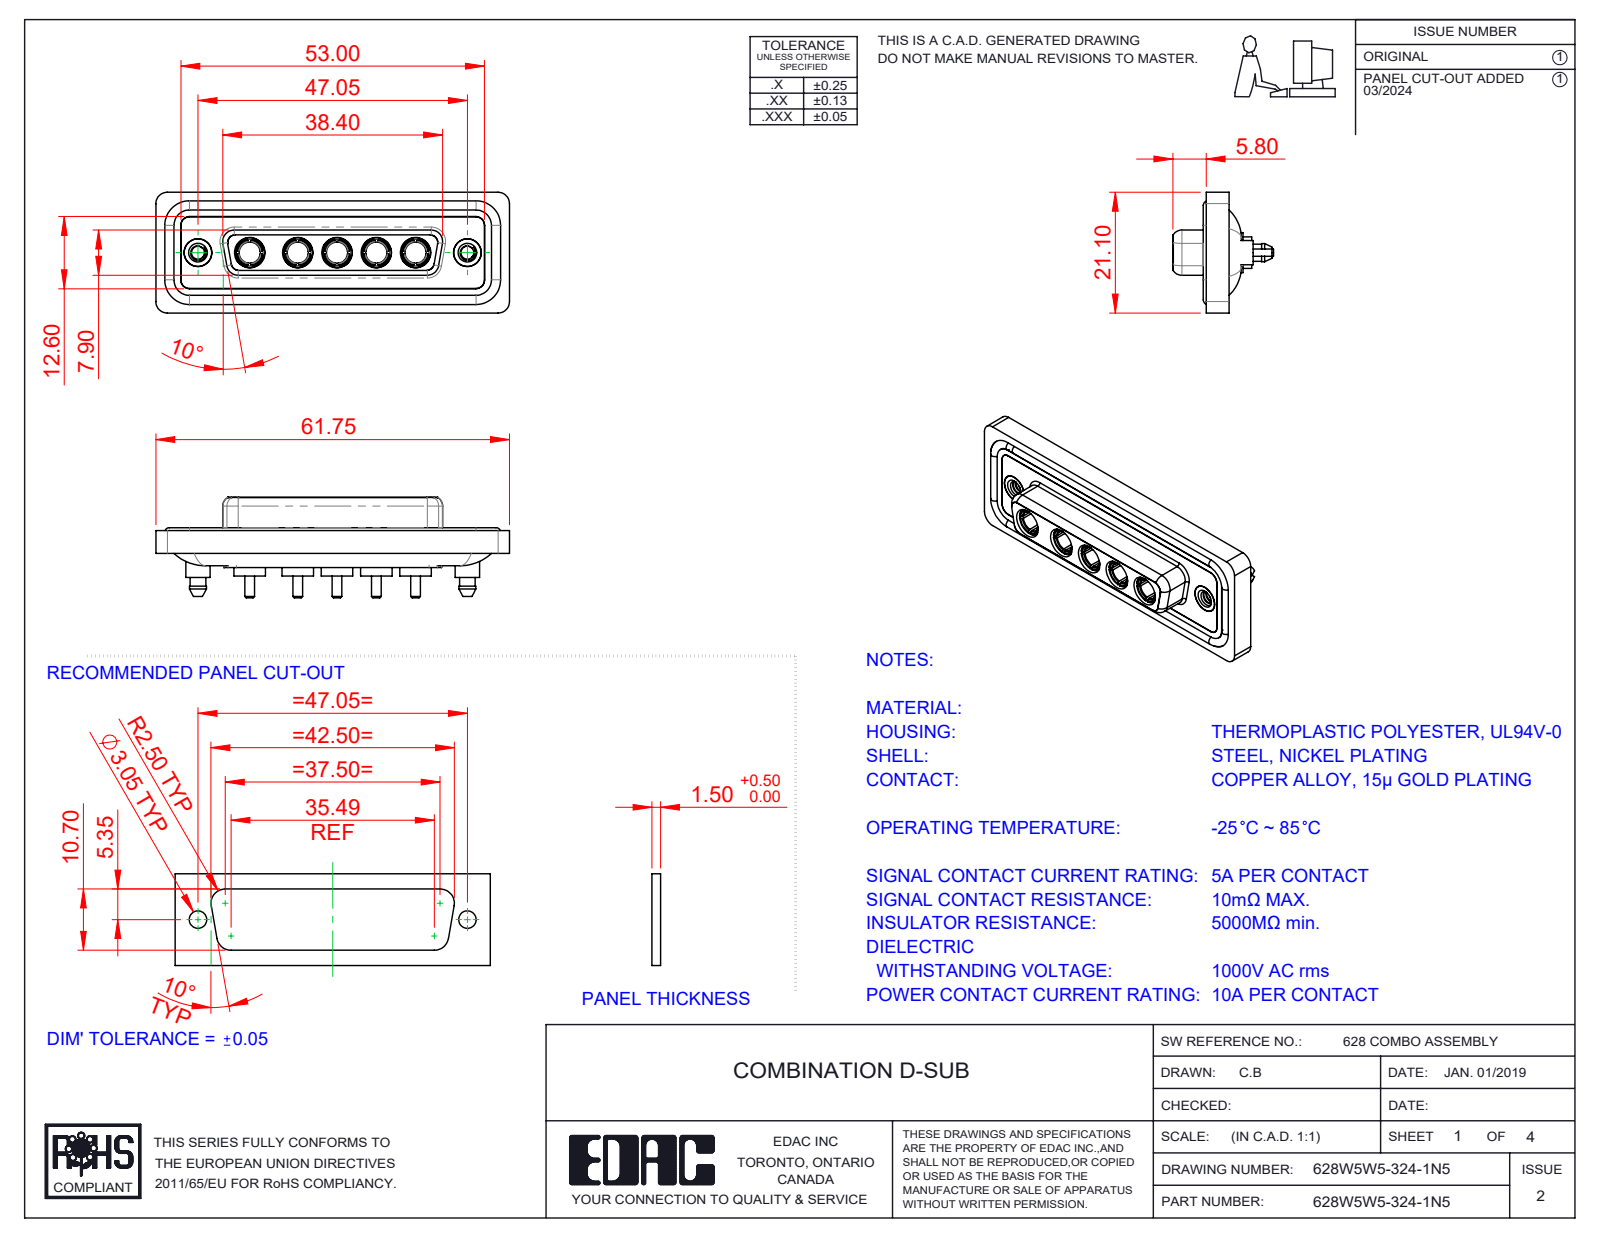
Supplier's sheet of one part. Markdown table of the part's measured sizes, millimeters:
| quantity | value |
| --- | --- |
| part name | 628Combo Housing_5W5; 628W5W5-324-1N5; 628Combo Waterproof Housing_25 Contacts; 628Combo Threaded Boardlock_5 (+3 more) |
| STEP written by | SolidWorks 2023 (CONFIG_CONTROL_DESIGN) |
| units | millimeters |
| bodies | 17 solids, 806 faces (266 planar, 335 cylindrical, 205 other) |
| overall size | 61.75 × 21.1 × 17.55 |
| volume | 8 233 mm³ |
| surface area | 13 685 mm² |
| round holes (diameter × count) | 4.85 × 7, 3.7 × 5, 5.3 × 5, 2.26 × 2, 4 × 2, 4.05 × 2, 5 × 2 |
| round bosses / shafts (diameter × count) | 5.5 × 5, 5.2 × 5, 4.96 × 5, 4.75 × 5, 3.75 × 5, 1.7 × 5, 1.6 × 4, 5.4 × 2 |
| partial cylindrical surfaces (radius × count) | 1.5 × 24, 2 × 18, 1.6 × 10, 1.35 × 8, 2.1 × 5, 0.25 × 4, 0.5 × 4, 0.6 × 4 |
| main face-to-face distances | 0.4, 1.8, 7.45, 5.65, 0.5, 7.05, 6.6, 1.6, 1.1, 1.5 |
| hole center spacings | 6.86, 9.04, 13.72, 38.01, 8.39, 15.25, 15.9, 17.43 |
